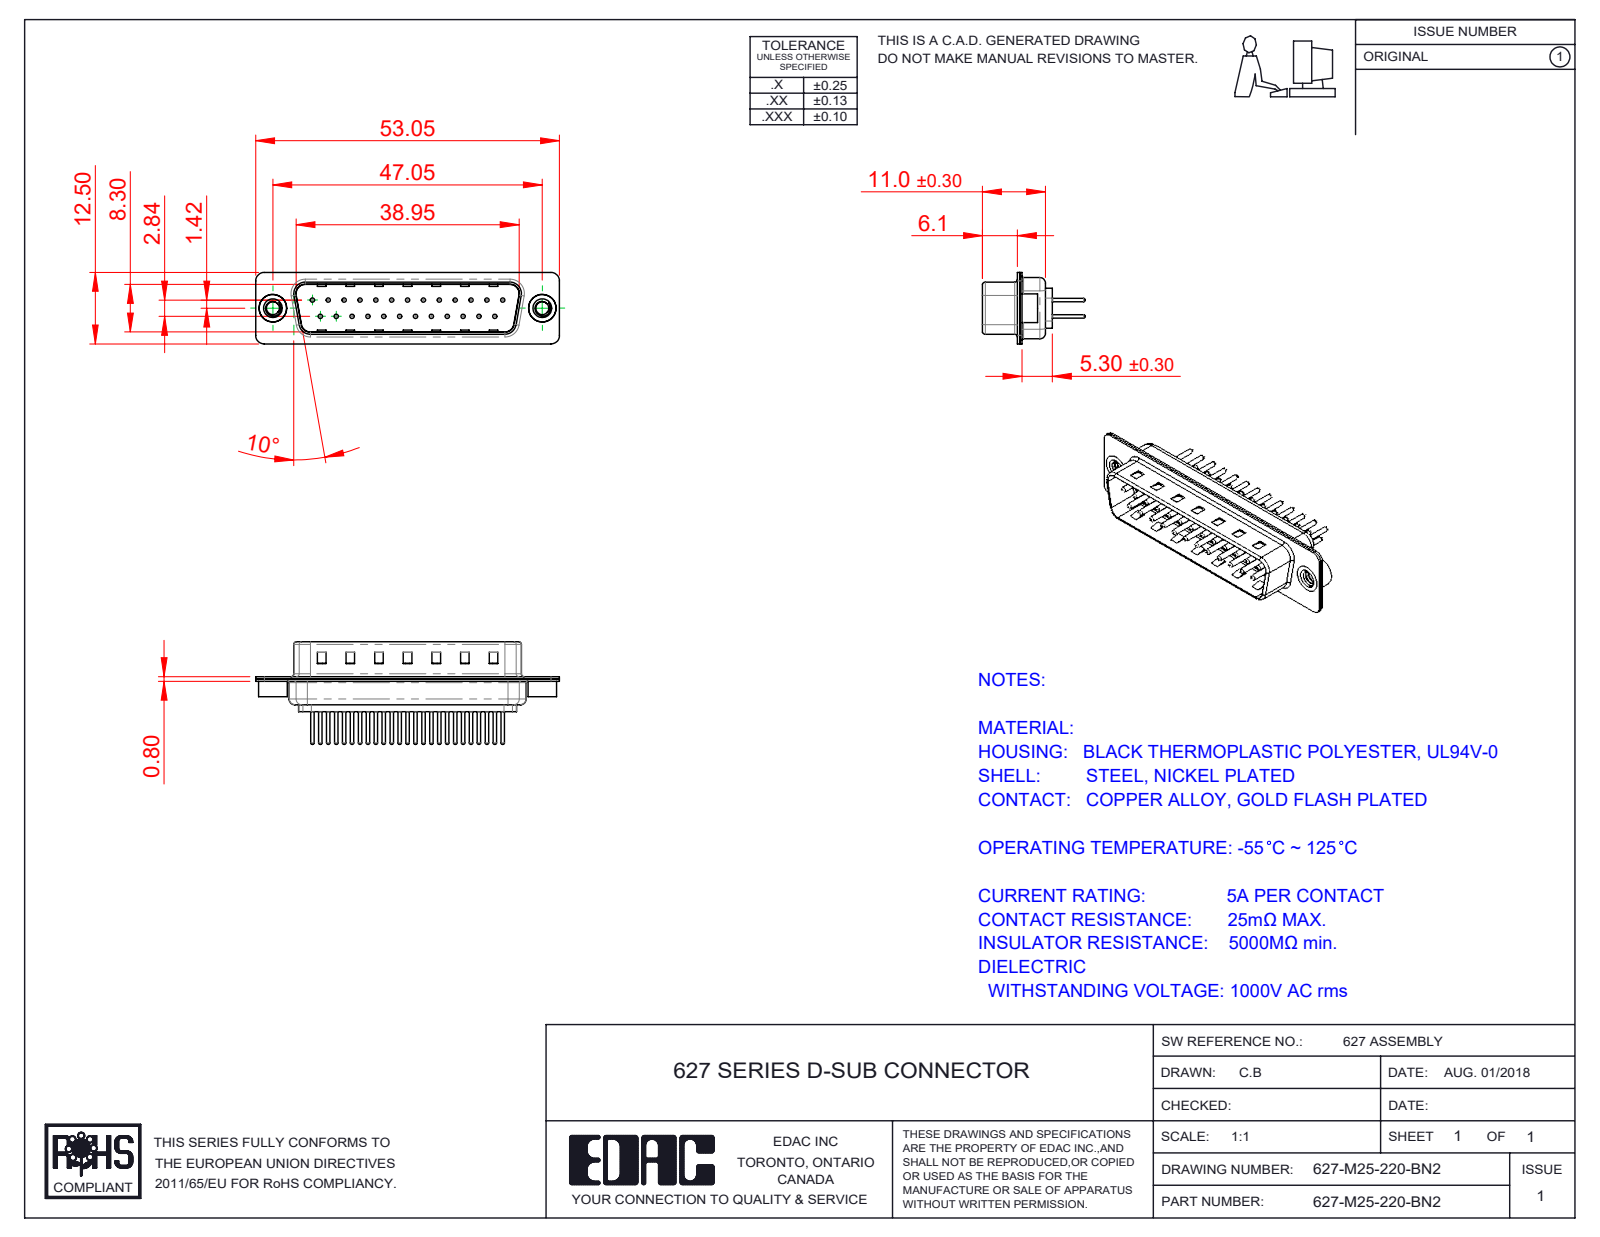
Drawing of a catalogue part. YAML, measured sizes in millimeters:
part_name: "627M 4-40 Threaded Rivet; 627-M25-220-BN2; 627M Contact Row 1_20; 627M Shell Rear_25 Contacts (+3 more)"
step_written_by: "SolidWorks 2020 (CONFIG_CONTROL_DESIGN)"
units: millimeters
bodies: {solids: 30, faces: 1301, planar: 346, cylindrical: 487, other: 468}
overall_size: [53.05, 17.9, 12.5]
volume: 2719
surface_area: 6843
round_holes:
  - {diameter: 0.75, count: 25}
  - {diameter: 1.6, count: 25}
  - {diameter: 2, count: 25}
  - {diameter: 2.26, count: 2}
  - {diameter: 4, count: 2}
  - {diameter: 4.8, count: 2}
round_bosses_or_shafts:
  - {diameter: 1.5, count: 25}
  - {diameter: 0.6, count: 25}
  - {diameter: 5, count: 2}
  - {diameter: 4.9, count: 2}
partial_cylinders:
  - {radius: 1.5, count: 16}
  - {radius: 2, count: 12}
  - {radius: 0.5, count: 8}
  - {radius: 1.6, count: 8}
  - {radius: 0.25, count: 4}
  - {radius: 0.6, count: 4}
  - {radius: 0.65, count: 4}
  - {radius: 0.9, count: 4}
face_to_face_distances: [0.4, 0.8, 9.5, 9.1, 8.7, 9.9, 1.2, 6.1, 5.7, 0.75]
hole_center_spacings: [3.16, 2.77, 5.54, 8.31, 11.08, 13.85, 16.62, 5.03]
